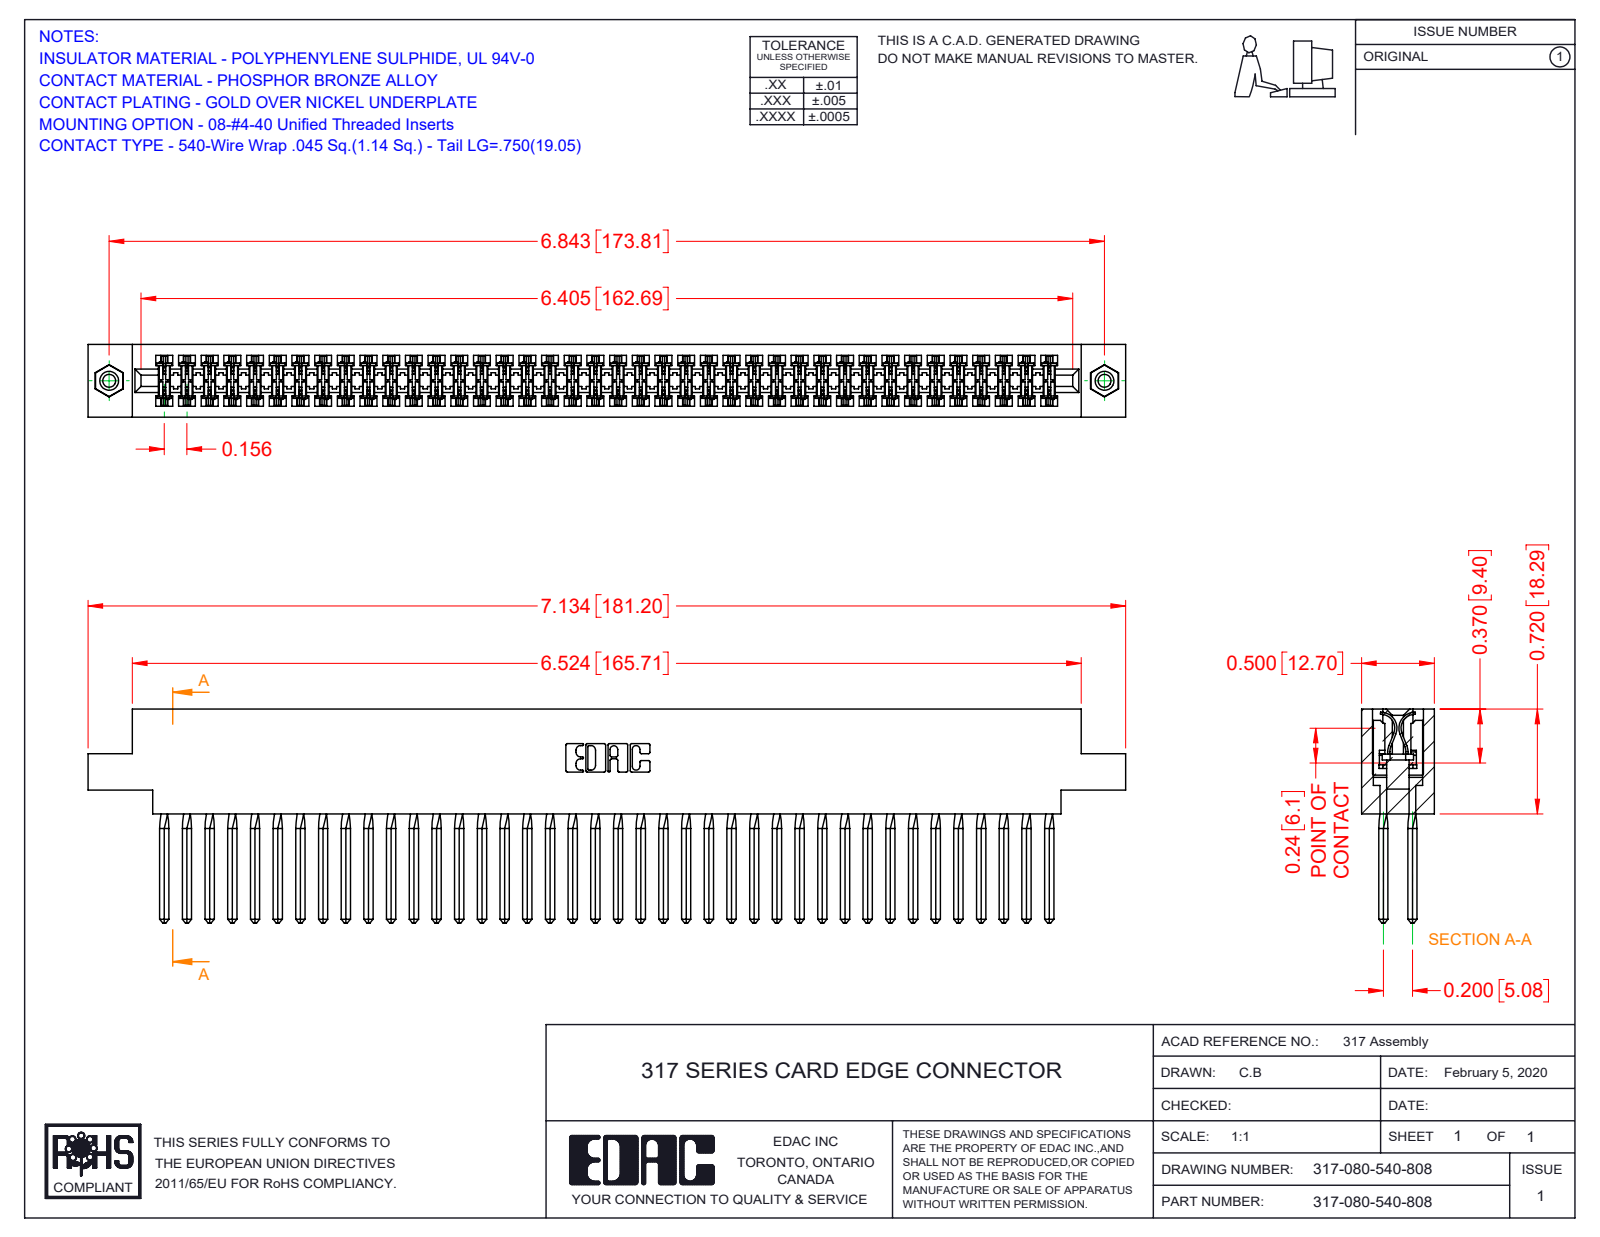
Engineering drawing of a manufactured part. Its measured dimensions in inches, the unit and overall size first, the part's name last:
Units: inches
Overall size (bounding box): 7.134 × 1.47 × 0.5
Round holes (diameter × count): ⌀0.089 ×2, ⌀0.125 ×2, ⌀0.156 ×2
Round bosses / shafts (diameter × count): ⌀0.155 ×2
Partial cylindrical surfaces — rounded edges, fillets, slot ends (radius × count): R0.015 ×160, R0.01 ×22, R0.007 ×6, R0.031 ×6, R0.026 ×3, R0.095 ×2, R0.1 ×2, R0.11 ×2
Main face-to-face distances: 0.5, 0.075, 0.425, 0.35, 0.195, 0.094, 0.2, 0.115, 0.131, 0.11
Hole centre spacings: 6.843
Volume: 1.851 in³ · Surface area: 70.02 in²
Bodies: 83 solids, 7282 faces (5930 planar, 1016 cylindrical, 336 other)
Part name (STEP PRODUCT): 317-290-001_540; 317-080-540-808; 345-250-001_345-250-003-102; 317 Part_.156 Dia - TI
STEP written by: SolidWorks 2016 (CONFIG_CONTROL_DESIGN)
